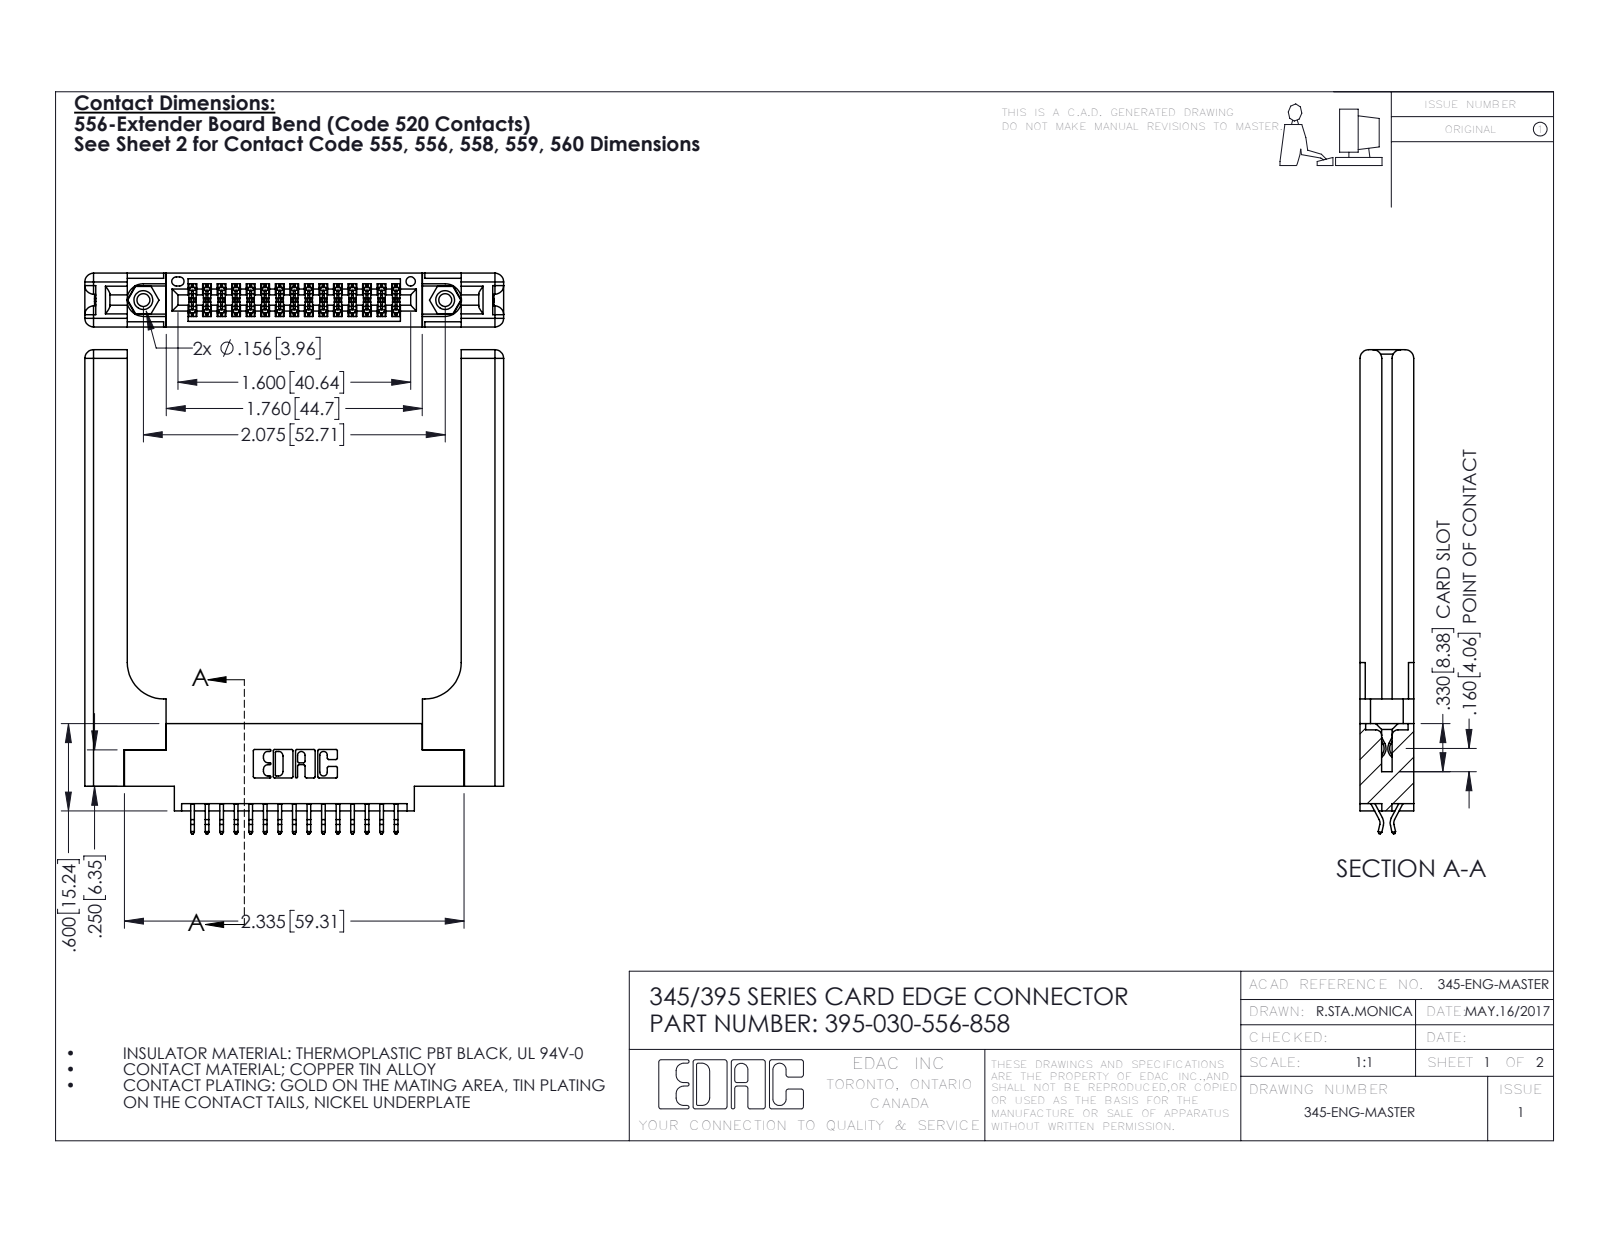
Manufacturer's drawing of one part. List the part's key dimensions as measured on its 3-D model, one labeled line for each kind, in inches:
Part name (STEP PRODUCT): 345 Part_0.170 Offset - 0.156 Dia-TH; 395-030-556-858; 345-250-001_345-250-001-102; 345-292-001_556 Tail (+1 more)
STEP written by: SolidWorks 2016 (CONFIG_CONTROL_DESIGN)
Units: inches
Bodies: 35 solids, 2066 faces (1342 planar, 664 cylindrical, 60 other)
Overall size (bounding box): 3.327 × 2.879 × 0.37
Volume: 0.928 in³ · Surface area: 22.65 in²
Round holes (diameter × count): ⌀0.089 ×2, ⌀0.125 ×2, ⌀0.156 ×2, ⌀0.064 ×1
Round bosses / shafts (diameter × count): ⌀0.155 ×2
Partial cylindrical surfaces — rounded edges, fillets, slot ends (radius × count): R0.006 ×45, R0.01 ×22, R0.06 ×16, R0.007 ×6, R0.031 ×6, R0.026 ×3, R0.01 ×2, R0.014 ×2
Main face-to-face distances: 0.37, 0.072, 0.298, 0.148, 0.15, 0.077, 0.22, 0.225, 0.025, 0.123
Hole centre spacings: 0.27, 1.842, 2.075
